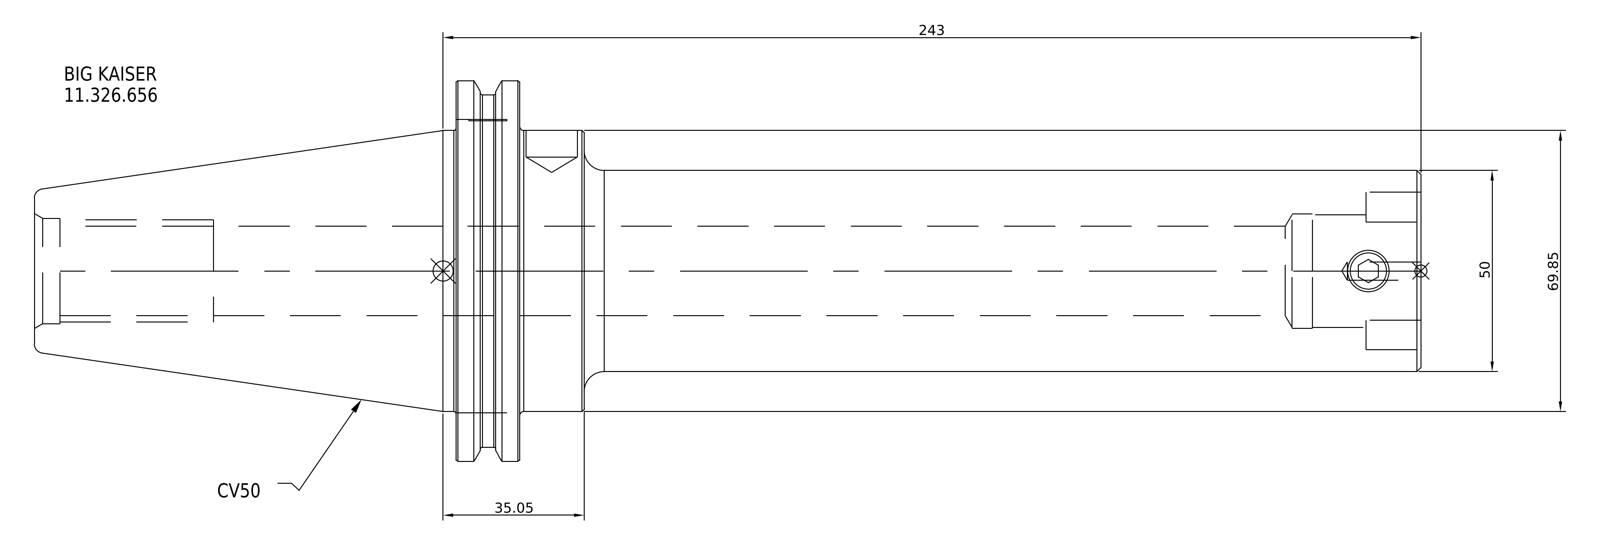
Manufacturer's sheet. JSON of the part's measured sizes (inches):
{"part_name": "11.326.656", "step_written_by": "SolidWorks 2021 (CONFIG_CONTROL_DESIGN)", "units": "inches", "bodies": {"solids": 1, "faces": 16, "planar": 7, "cylindrical": 6, "other": 3}, "overall_size": [13.567, 3.875, 3.875], "volume_in3": 51.92, "surface_area_in2": 114.2, "round_bosses_or_shafts": [[3.875, 1], [3.594, 1], [2.75, 1], [1.969, 1]], "face_to_face_distances": [0.691, 8.817, 9.508, 8.189, 0.628, 1.319, 13.567, 5.378, 4.75, 4.059]}
